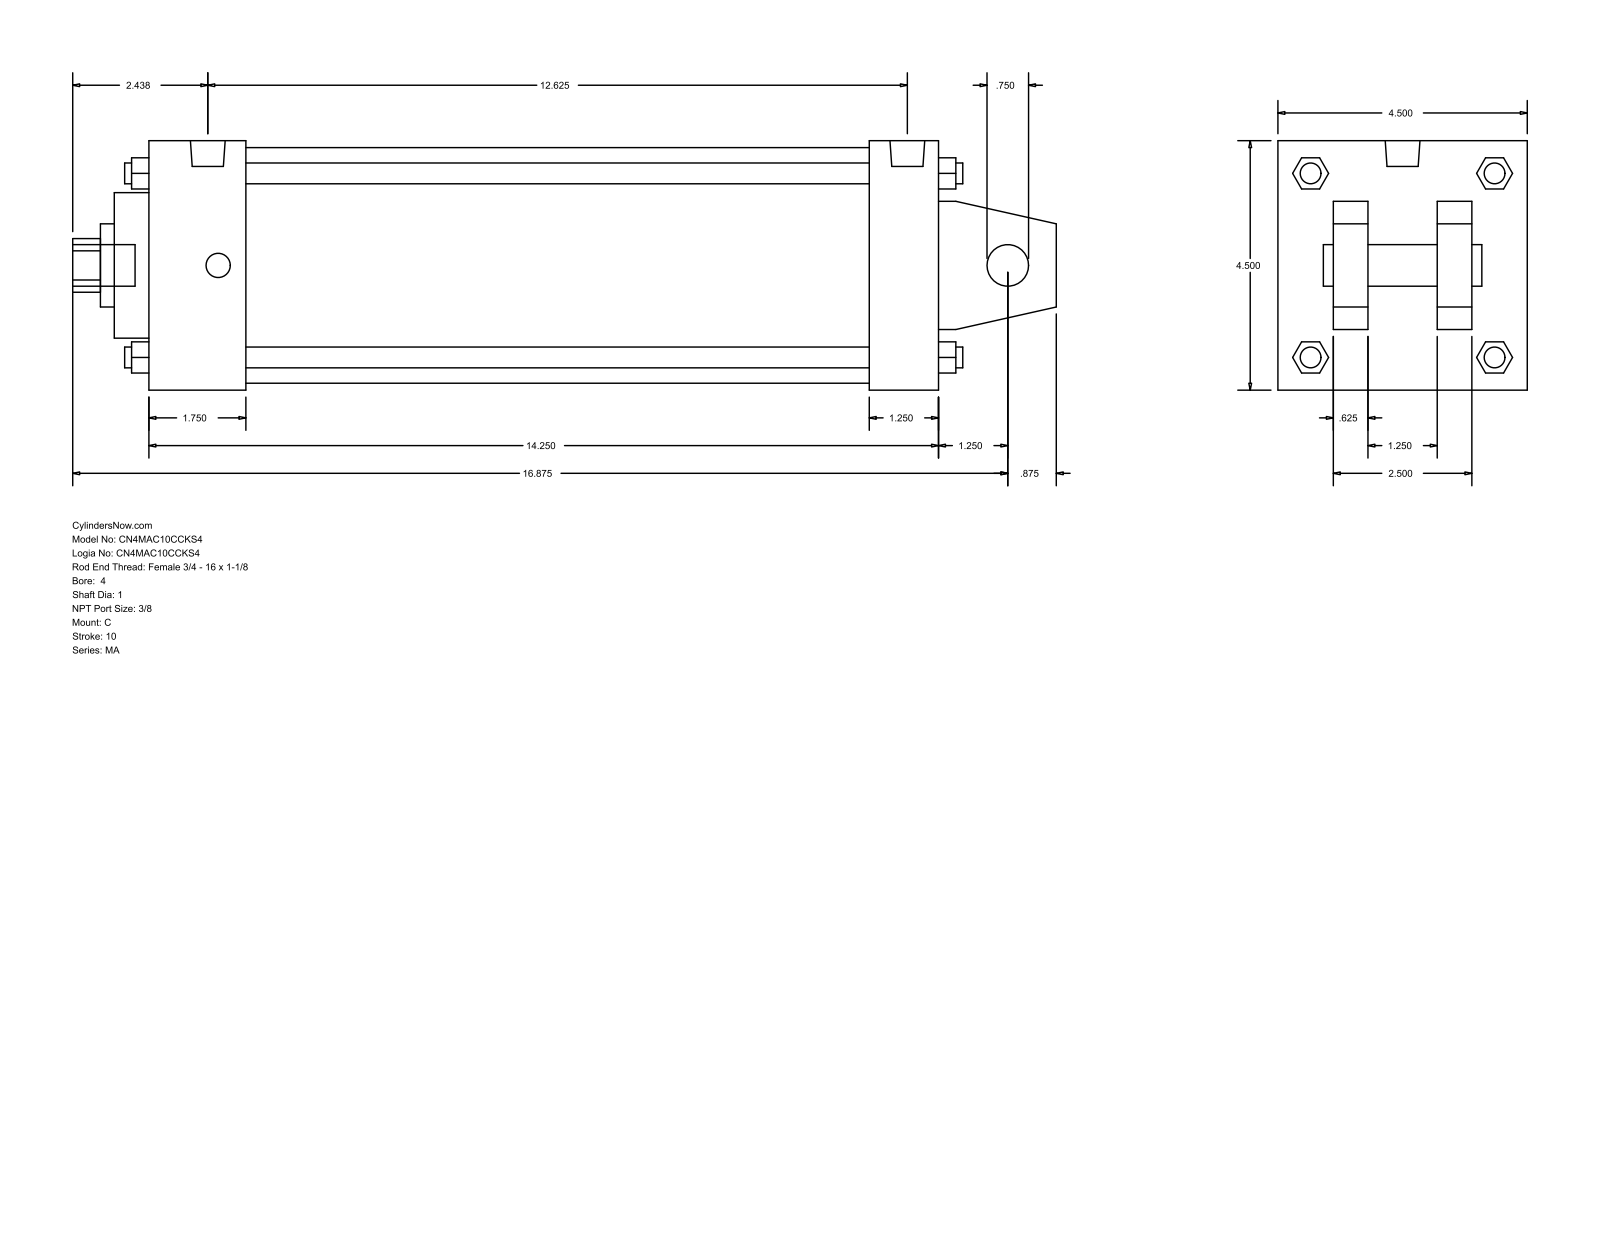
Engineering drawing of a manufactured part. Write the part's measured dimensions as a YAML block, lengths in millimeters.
part_name: "MA_C__0400_1"
step_written_by: "GSSL Pune (CONFIG_CONTROL_DESIGN)"
units: millimeters
bodies: {solids: 0, faces: 141, planar: 109, cylindrical: 32, other: 0}
overall_size: [450.85, 114.3, 114.3]
round_holes:
  - {diameter: 19.05, count: 1}
  - {diameter: 25.4, count: 1}
  - {diameter: 38.1, count: 1}
  - {diameter: 66.67, count: 1}
  - {diameter: 107.95, count: 1}
round_bosses_or_shafts:
  - {diameter: 11.11, count: 4}
  - {diameter: 9.53, count: 4}
  - {diameter: 15.93, count: 2}
  - {diameter: 19.05, count: 1}
partial_cylinders:
  - {radius: 12.29, count: 1}
face_to_face_distances: [114.3, 361.96, 15.87, 31.76, 73.03, 41.27, 25.4, 88.9, 47.63, 330.2]
